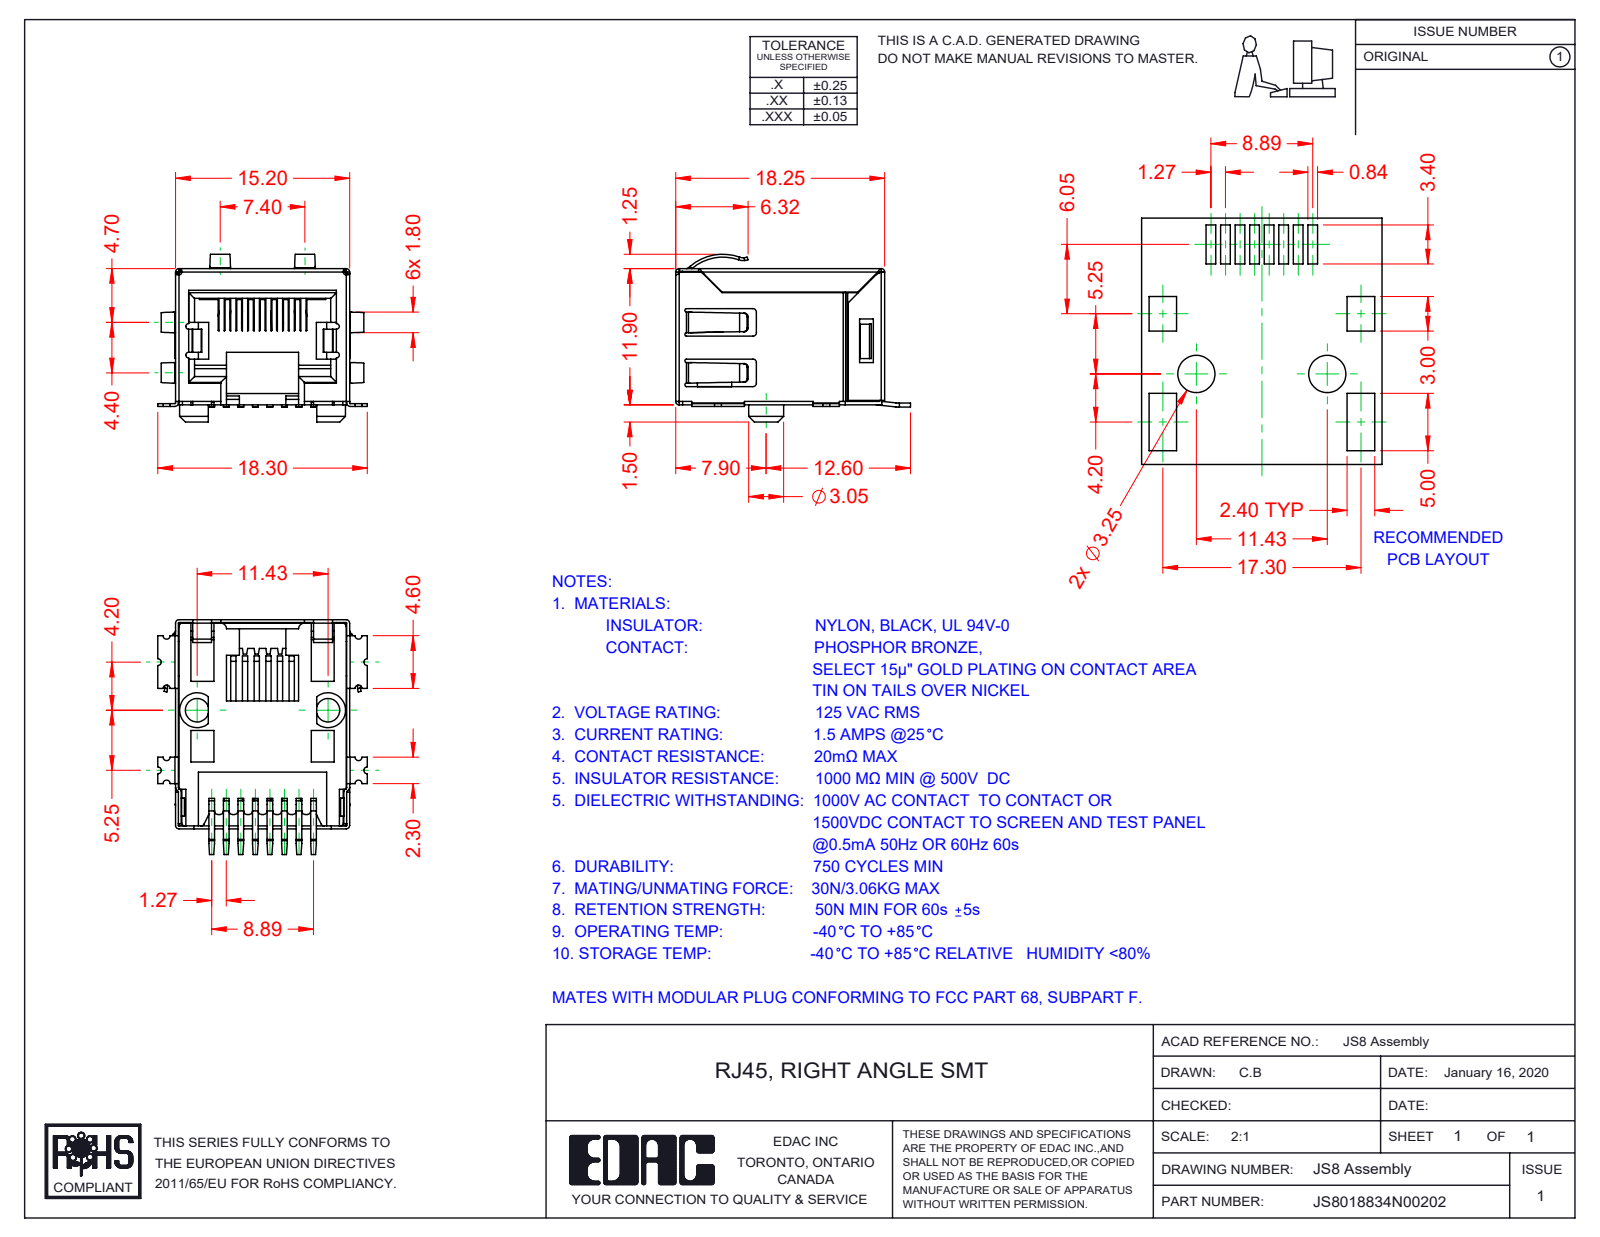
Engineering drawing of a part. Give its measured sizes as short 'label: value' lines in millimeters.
name: S8 Insulator; S8 Shield; S8 Contacts; RJS8018834N00202
written by: SolidWorks 2016 (CONFIG_CONTROL_DESIGN)
unit: mm
bodies: 10 solids, 976 faces (602 planar, 314 cylindrical, 60 other)
size: 20.5 × 18.3 × 14.65
volume: 1 308 mm³; area: 4 634 mm²
rounds: 59× R0.3, 19× R0.25, 18× R0.5, 17× R0.2, 8× R0.15, 7× R0.75, 4× R1, 3× R1.25
face distances: 14.65, 14.95, 14.9, 1, 0.35, 14.7, 0.75, 10.9, 1.1, 15.2
